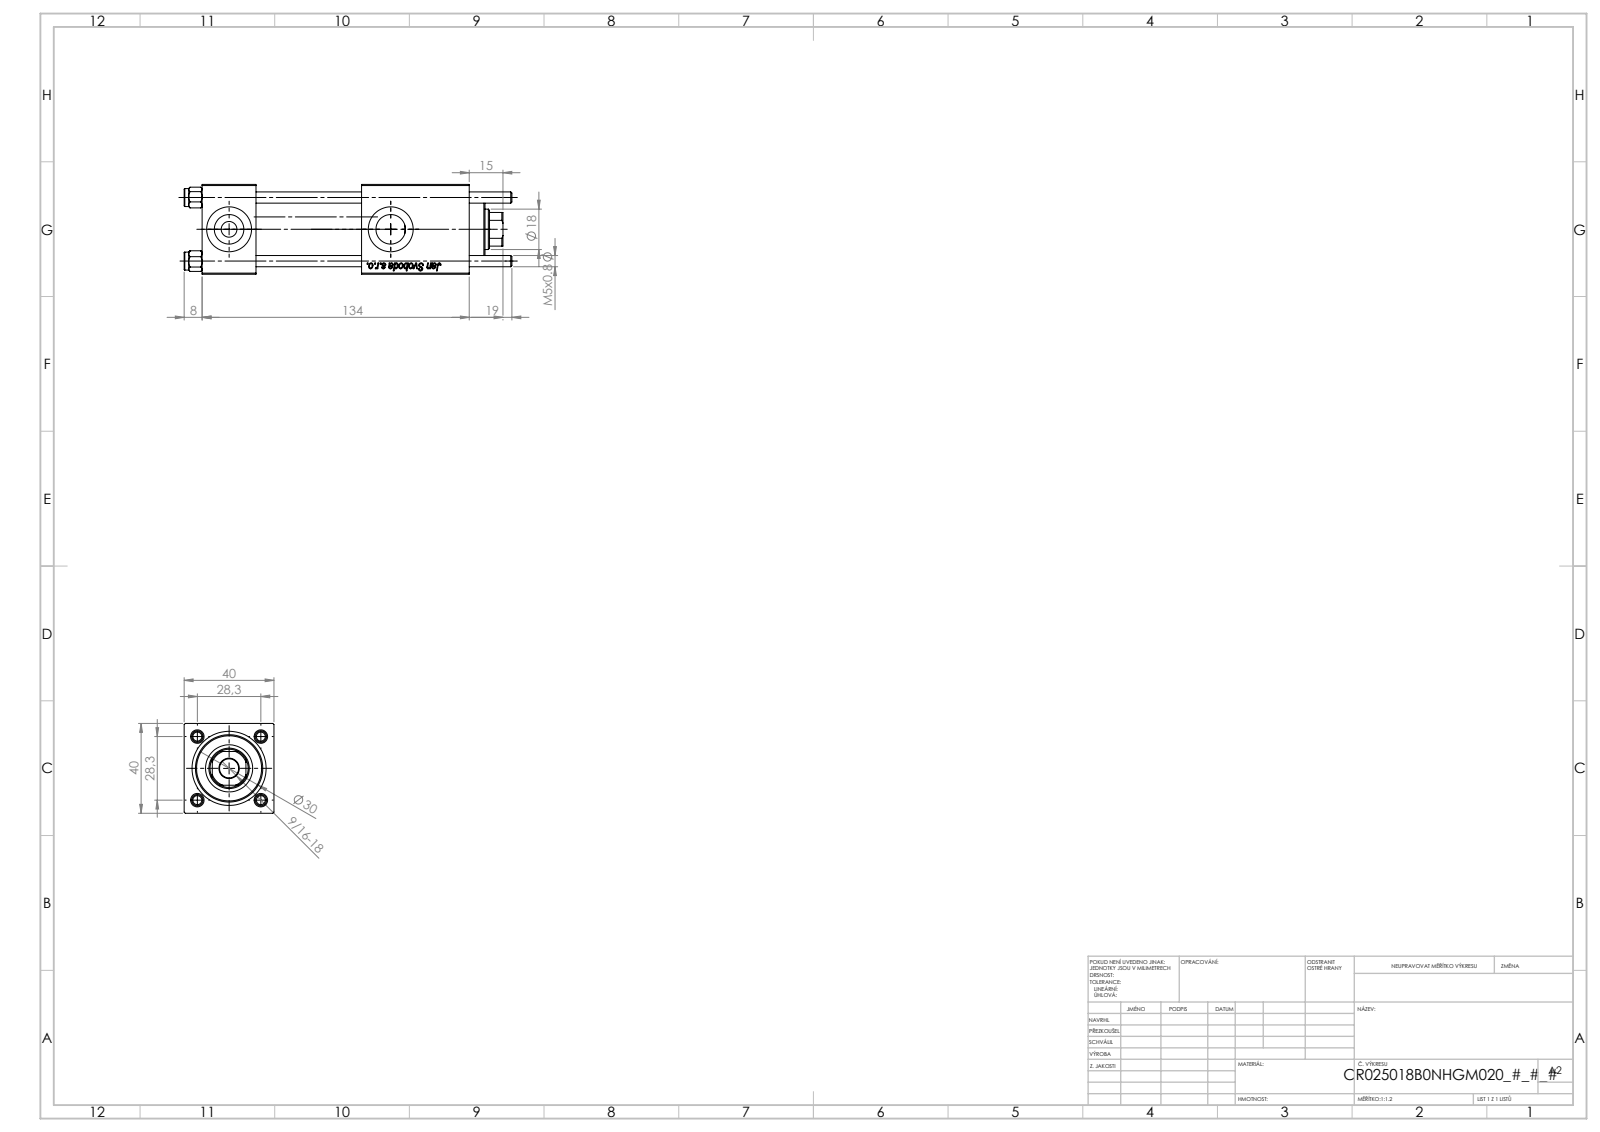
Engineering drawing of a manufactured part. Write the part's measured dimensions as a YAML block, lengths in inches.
part_name: "V215CR_VCP_B; NUT_M5_B; V215CR_B-1; V215CR_B_TYCINKA (+1 more)"
step_written_by: "SolidWorks 2019 (CONFIG_CONTROL_DESIGN)"
units: inches
bodies: {solids: 11, faces: 1152, planar: 428, cylindrical: 76, other: 648}
overall_size: [5.748, 1.575, 1.575]
volume: 9.306
surface_area: 94.39
round_holes:
  - {diameter: 0.197, count: 4}
  - {diameter: 0.787, count: 3}
  - {diameter: 0.276, count: 2}
  - {diameter: 0.518, count: 2}
  - {diameter: 0.335, count: 1}
  - {diameter: 0.709, count: 1}
  - {diameter: 0.827, count: 1}
  - {diameter: 0.984, count: 1}
  - {diameter: 1.181, count: 1}
round_bosses_or_shafts:
  - {diameter: 0.315, count: 4}
  - {diameter: 1.22, count: 1}
partial_cylinders:
  - {radius: 0.335, count: 1}
face_to_face_distances: [1.575, 0.945, 2.795, 1.85, 3.555, 2.61, 0.76, 4.685, 3.74, 1.89]
hole_center_spacings: [0.788, 1.114, 1.576, 2.835]
